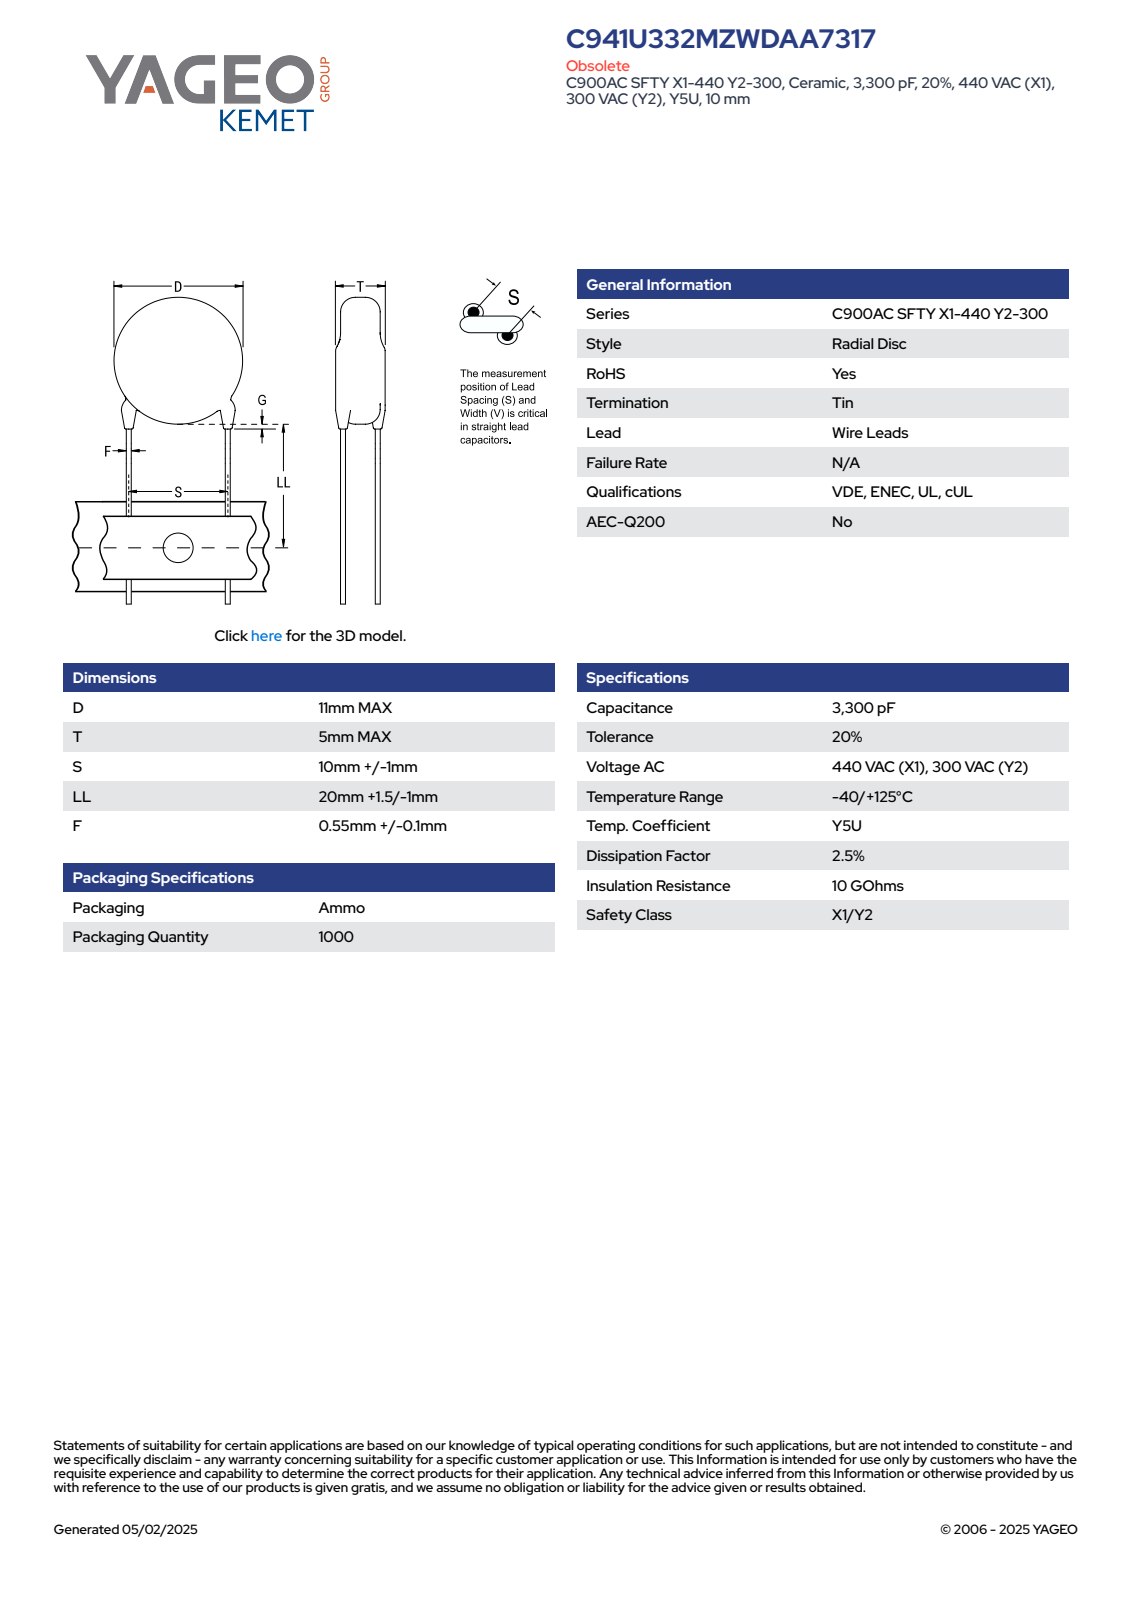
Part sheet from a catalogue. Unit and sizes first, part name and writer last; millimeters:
Units: millimetres
Overall size (bounding box): 32.5 × 11 × 5
Round bosses / shafts (diameter × count): ⌀0.65 ×2, ⌀11 ×1
Main face-to-face distances: 5, 1.27, 27.63, 26.36, 0.35, 1.03, 5.19, 0.79, 3.77, 3.92
Volume: 479 mm³ · Surface area: 440 mm²
Bodies: 4 solids, 83 faces (61 planar, 6 cylindrical, 16 other)
Part name (STEP PRODUCT): CCD_STC900_D11T5S10LL21.5F0.65G3
STEP written by: SolidWorks 2014 (AUTOMOTIVE_DESIGN)
